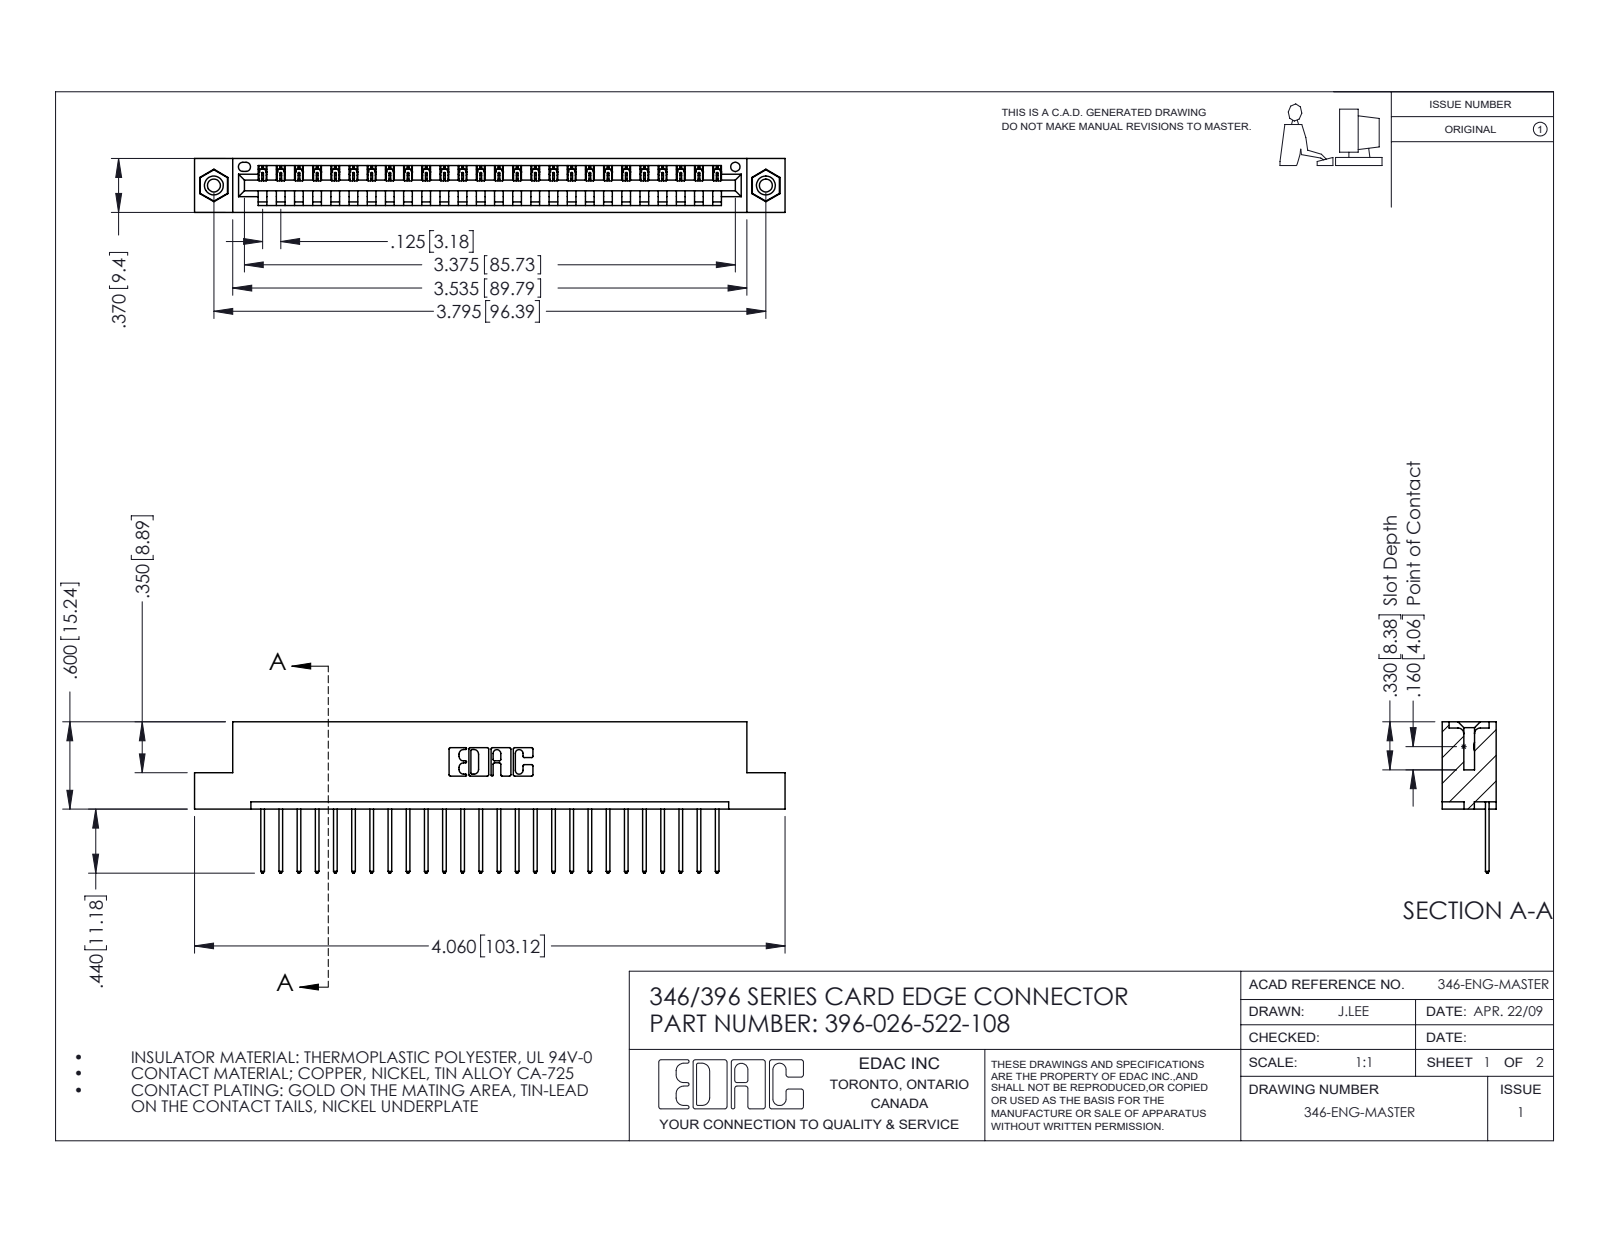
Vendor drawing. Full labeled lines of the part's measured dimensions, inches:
Part name (STEP PRODUCT): 345-250-001_345-250-003-102; 346 Part_Flush Mounting Lugs - 0.156 Dia-TI; 345-292-001_345-293-122; 396-026-522-108
STEP written by: SolidWorks 2016 (CONFIG_CONTROL_DESIGN)
Units: inches
Bodies: 29 solids, 1690 faces (1148 planar, 526 cylindrical, 16 other)
Overall size (bounding box): 4.06 × 1.04 × 0.37
Volume: 0.595 in³ · Surface area: 18.82 in²
Round holes (diameter × count): ⌀0.089 ×2, ⌀0.125 ×2, ⌀0.156 ×2, ⌀0.064 ×1
Round bosses / shafts (diameter × count): ⌀0.155 ×2
Partial cylindrical surfaces — rounded edges, fillets, slot ends (radius × count): R0.006 ×52, R0.01 ×52, R0.01 ×22, R0.007 ×6, R0.031 ×6, R0.026 ×3, R0.031 ×2, R0.04 ×2
Main face-to-face distances: 0.048, 0.322, 0.25, 0.37, 0.072, 0.298, 0.025, 0.148, 0.222, 0.1
Hole centre spacings: 0.246, 3.587, 3.795
